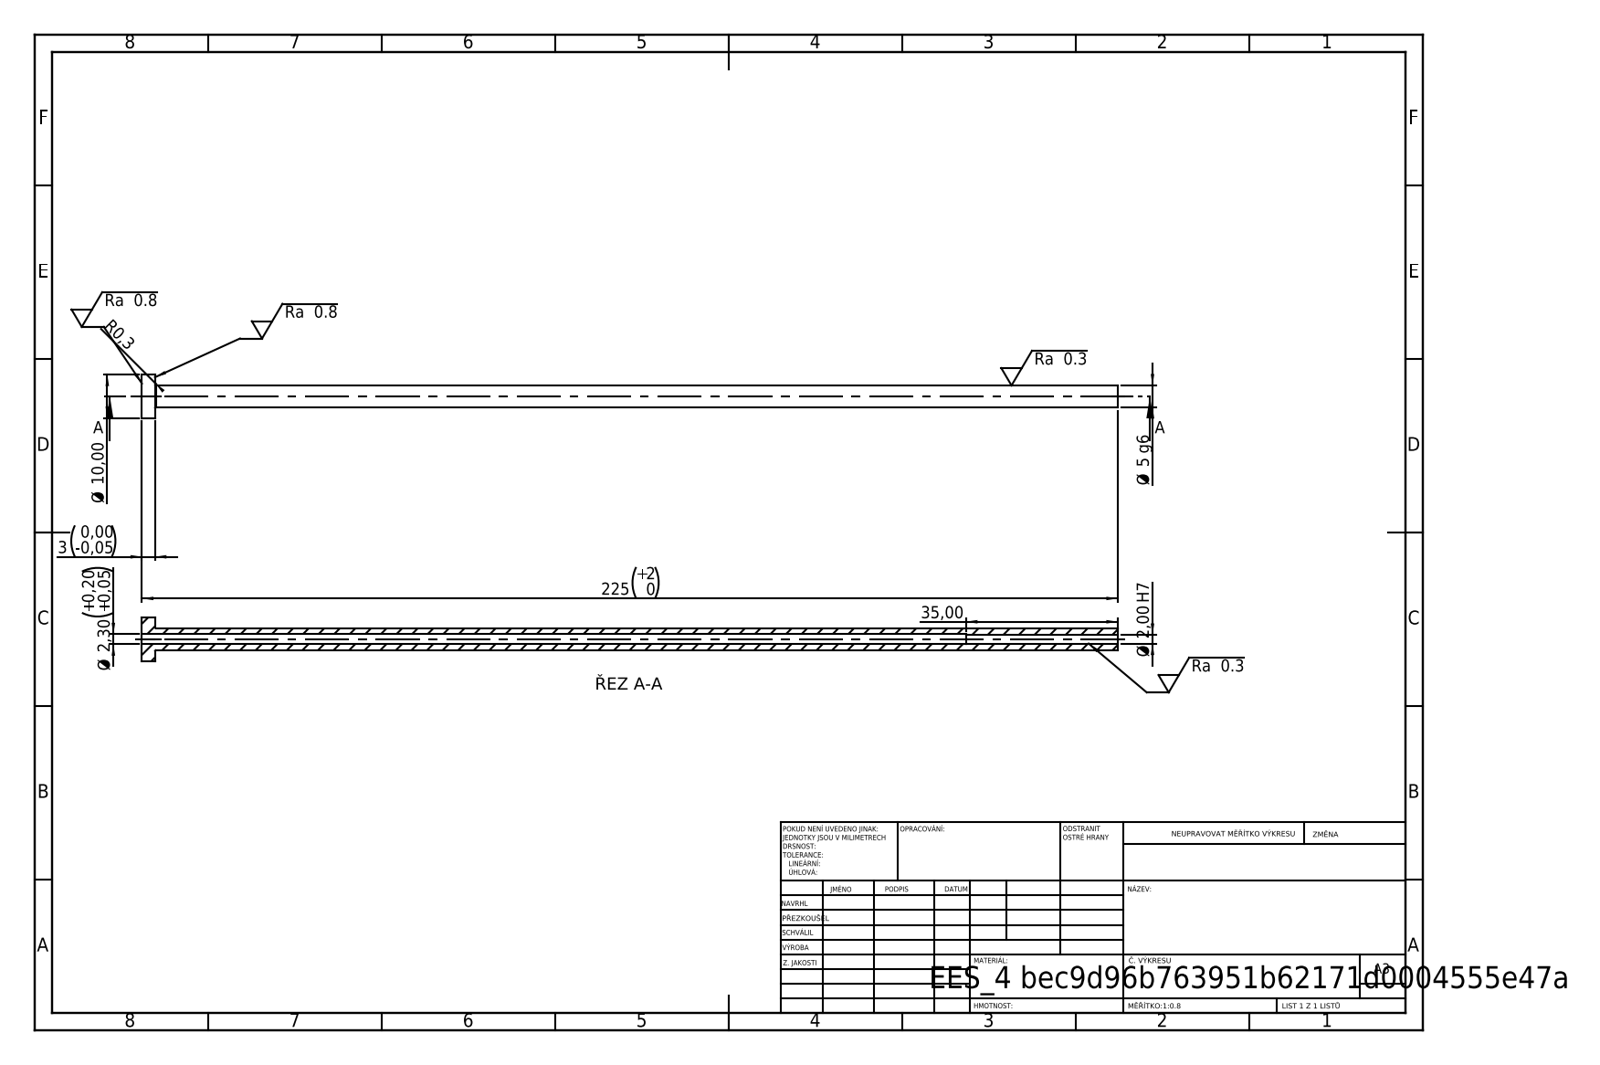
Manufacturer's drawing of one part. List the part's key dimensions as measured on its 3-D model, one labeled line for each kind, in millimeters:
STEP written by: SolidWorks 2019 (CONFIG_CONTROL_DESIGN)
Units: millimetres
Bodies: 1 solid, 14 faces (4 planar, 8 cylindrical, 2 other)
Overall size (bounding box): 225 × 10 × 10
Volume: 3 696 mm³ · Surface area: 5 323 mm²
Round holes (diameter × count): ⌀2 ×1, ⌀2.3 ×1
Round bosses / shafts (diameter × count): ⌀10 ×1, ⌀5 ×1
Main face-to-face distances: 3, 225, 222, 190, 187, 35
